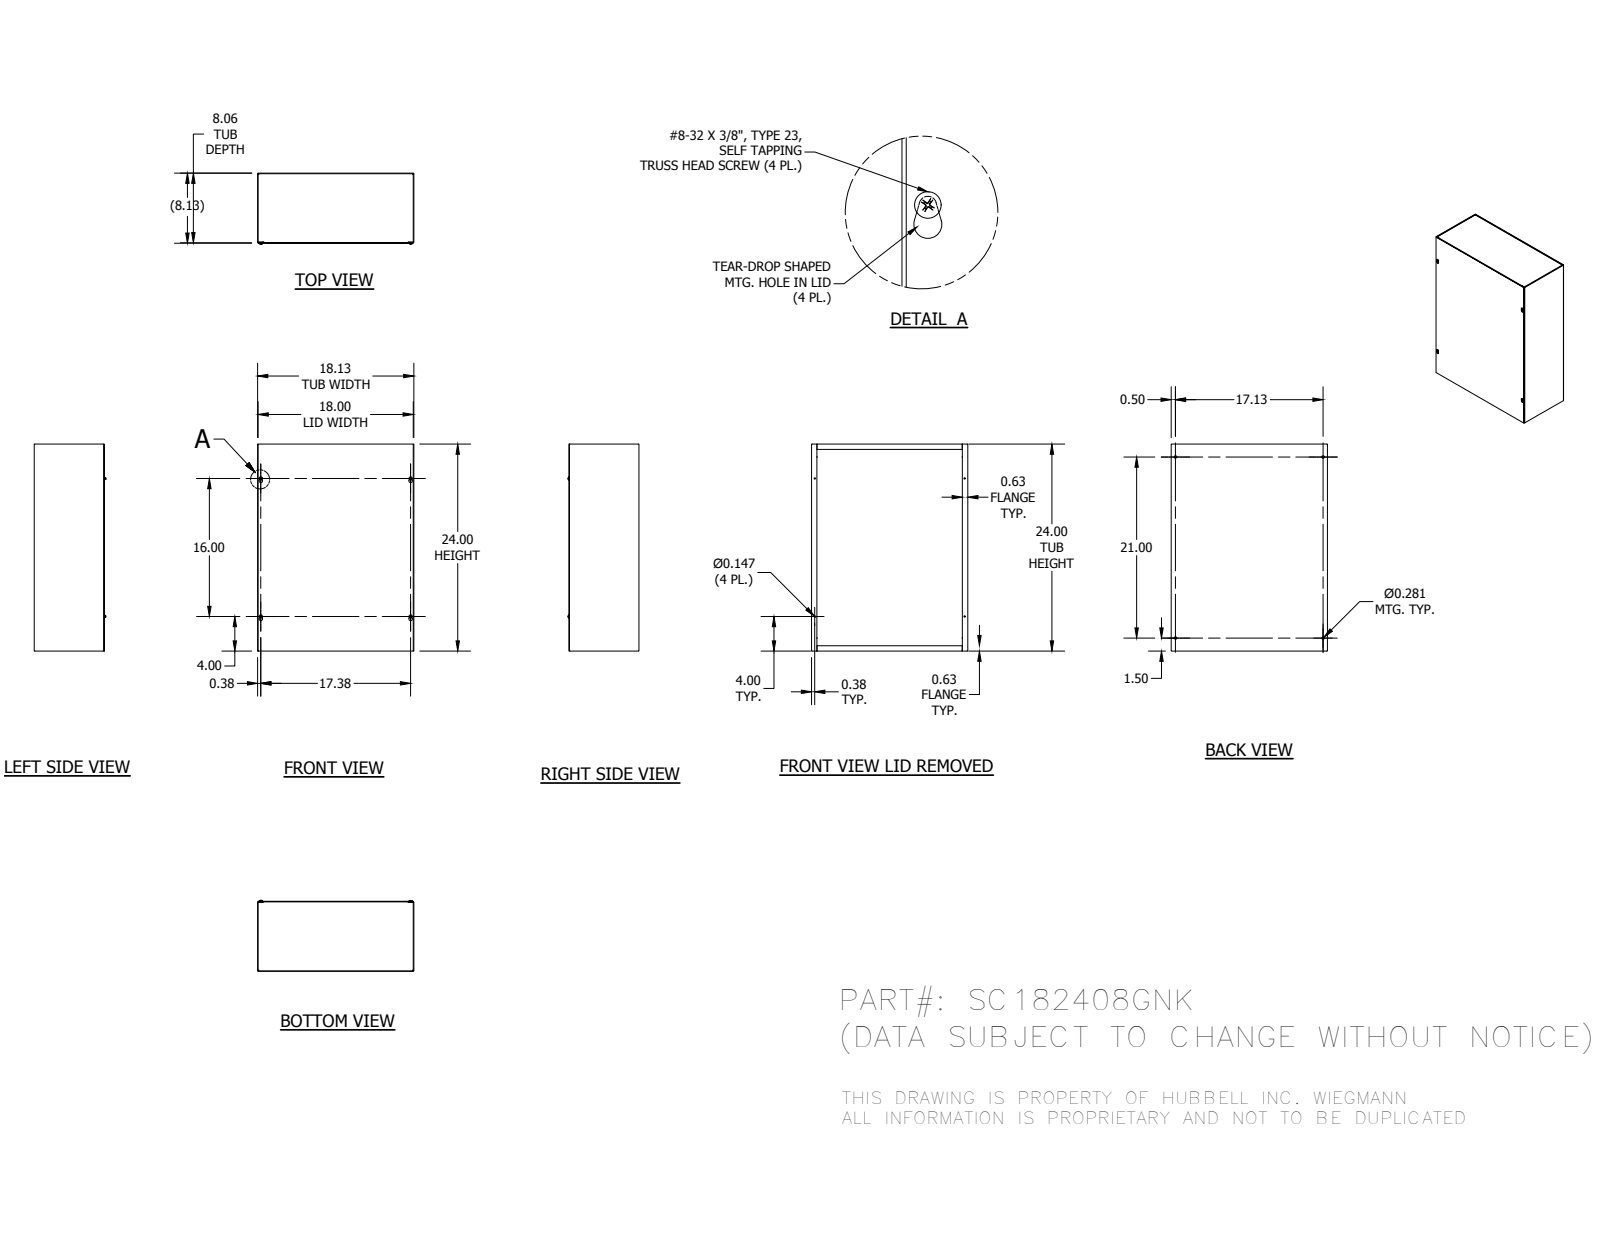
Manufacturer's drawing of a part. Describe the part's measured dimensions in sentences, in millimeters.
The part is named "SC182408GNKBLR; SC1808GNKTB; SC1824GLPA; 34056 (+1 more)". Its 3-D file was written by "Autodesk Inventor 2014 (AUTOMOTIVE_DESIGN)". It is 8 solids with 268 faces: 152 planar, 48 cylindrical and 68 other. Overall it measures 609.6 by 460.38 by 208.92 millimeters. Its volume is 1 658 000 cubic millimeters and its surface area 2 102 000 square millimeters. Round holes: 4 of diameter 3.73, 4 of diameter 7.14. Round bosses or shafts: 4 of diameter 9.75, 4 of diameter 4.17. Partial cylindrical surfaces (rounded edges, fillets, slot ends): 12 of radius 0.4, 12 of radius 1.98, 4 of radius 3.17, 4 of radius 5.16. The main face-to-face distances are 1.59, 203.2, 1.58, 204.78, 204.79, 206.37, 458.79, 608.01, 457.2, 460.38. The hole center spacings are 63.58, 442.73, 469.91, 642.48, 406.4, 434.98, 441.32, 533.4.
